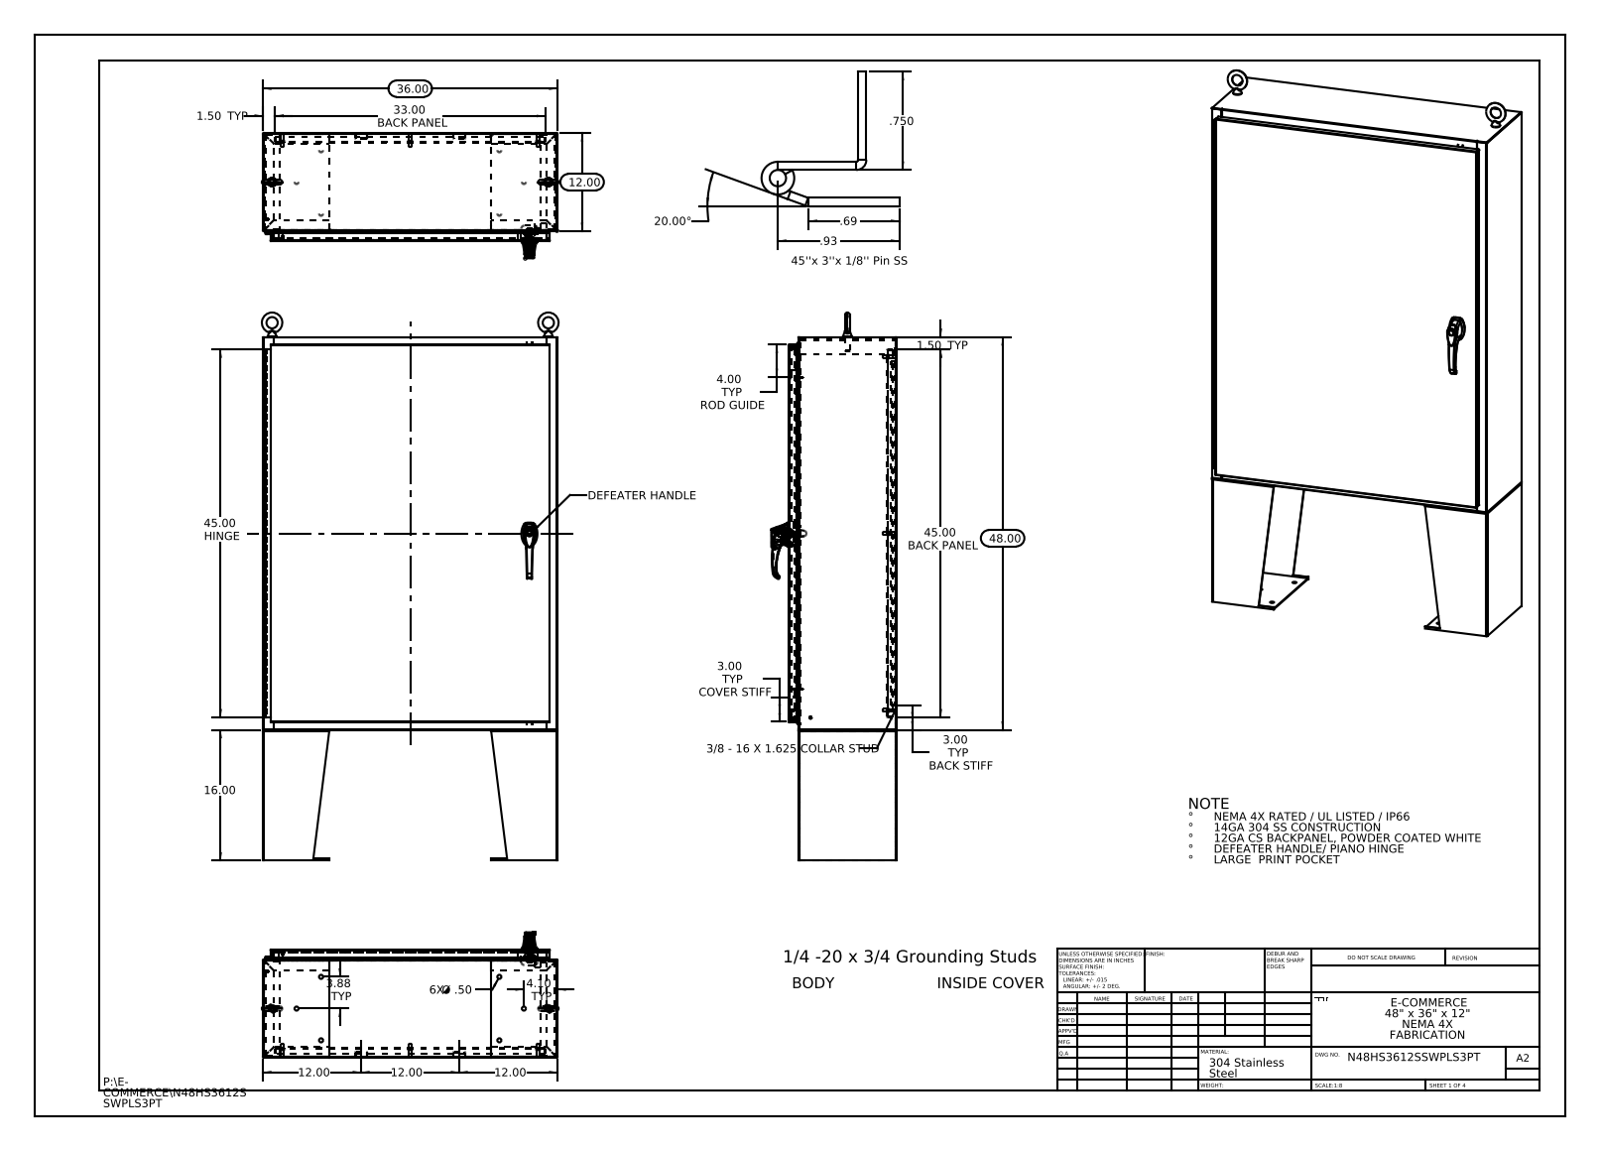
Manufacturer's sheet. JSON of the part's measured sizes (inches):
{"part_name": "N48HS3612SSWPLS3PT SD-LSK-ASSY; N48HS3612SSWPLS3PT Defeater Handle Rod; N48HS3612SSWPLS3PT Hinge Enclosure Side2; N48HS3612SSWPLS3PT Backpanel (+8 more)", "step_written_by": "SolidWorks 2013 (CONFIG_CONTROL_DESIGN)", "units": "inches", "bodies": {"solids": 55, "faces": 3520, "planar": 1385, "cylindrical": 1317, "other": 818}, "overall_size": [67, 36.271, 15.307], "volume_in3": 781.7, "surface_area_in2": 18668, "round_holes": [[0.5, 14], [0.25, 10], [0.75, 4], [0.138, 3], [0.161, 3], [0.079, 2], [0.203, 2], [0.313, 2], [0.437, 2], [0.125, 1], [0.125, 1], [0.197, 1]], "round_bosses_or_shafts": [[0.625, 10], [0.157, 10], [0.14, 10], [0.375, 8], [0.33, 8], [0.315, 3], [0.236, 3], [1.181, 1]], "partial_cylinders_radius": [[0.118, 37], [0.013, 34], [0.006, 33], [0.088, 28], [0.039, 15], [0.028, 12], [0.039, 8], [0.143, 8]], "face_to_face_distances": [0.075, 13.126, 0.104, 13.051, 1.075, 13.201, 1, 12.126, 12.051, 1.179], "hole_center_spacings": [7.137, 13.578, 17.357, 19.665, 21.625, 25.094, 38.003, 40.993]}
